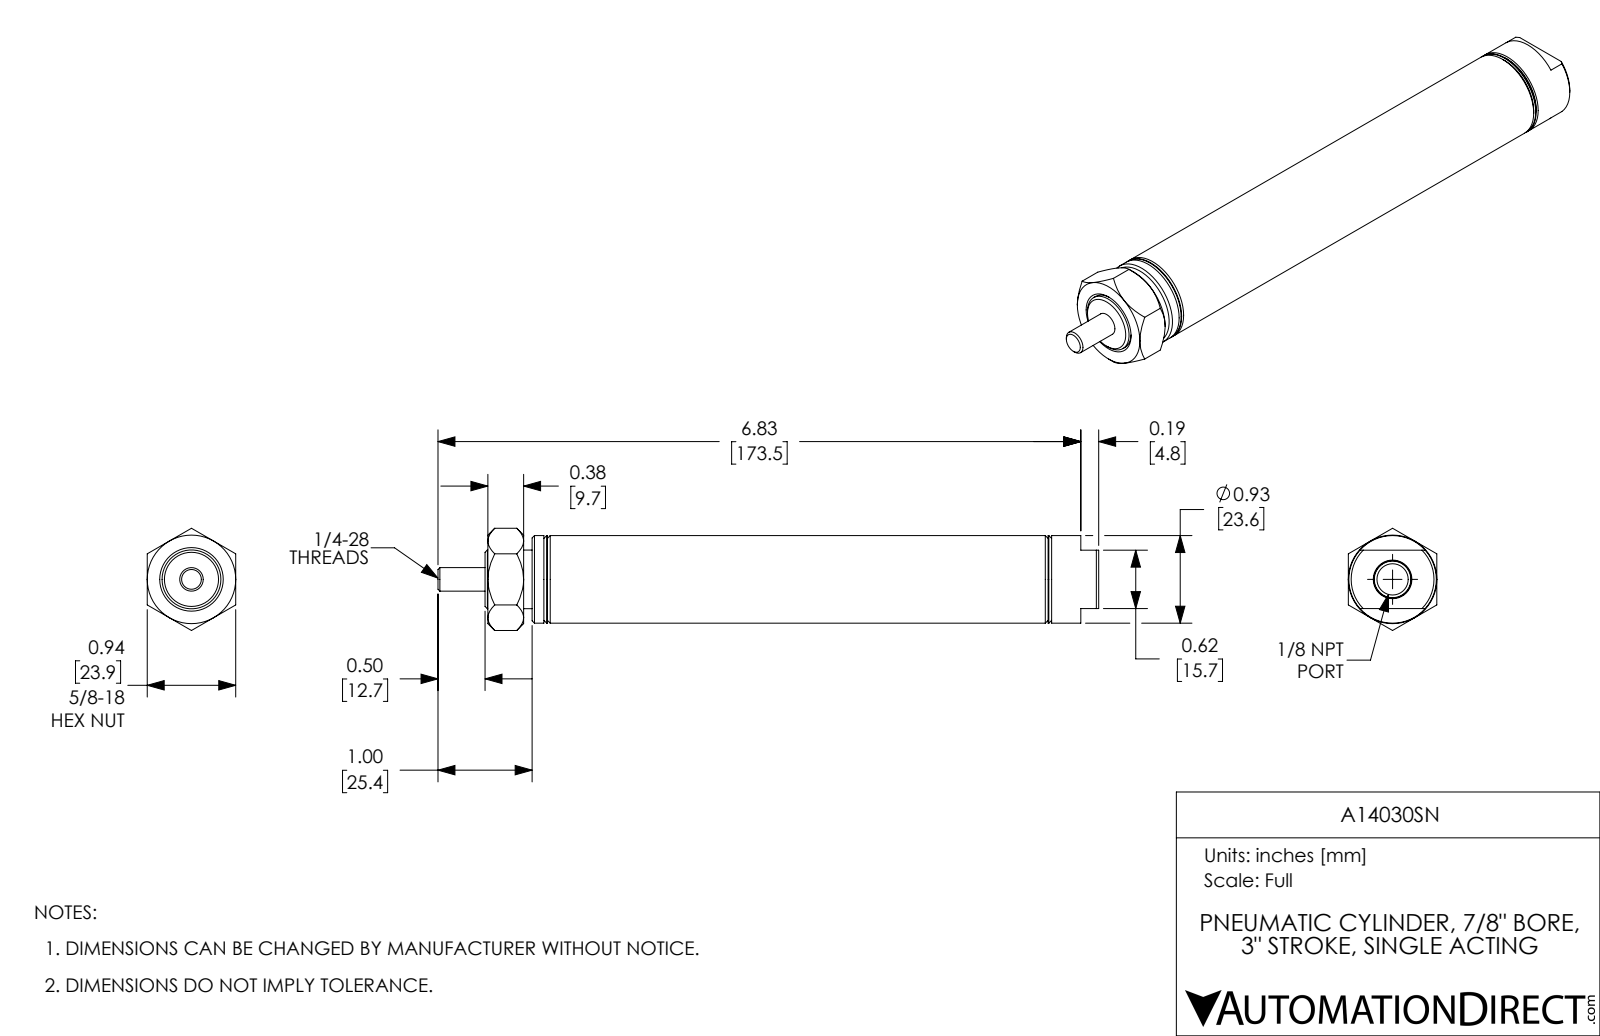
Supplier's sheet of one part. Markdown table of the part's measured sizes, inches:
| quantity | value |
| --- | --- |
| part name | A14030SN_Main Body; A14030SN; A14030SN_Mounting Nut_D-9; A14030SN_Rod |
| STEP written by | SolidWorks 2017 (AUTOMOTIVE_DESIGN) |
| units | inches |
| bodies | 3 solids, 94 faces (27 planar, 28 cylindrical, 39 other) |
| overall size | 7.02 × 1.085 × 0.94 |
| volume | 2.719 in³ |
| surface area | 41.83 in² |
| round holes (diameter × count) | 0.25 × 1, 0.332 × 1, 0.625 × 1, 0.875 × 1 |
| round bosses / shafts (diameter × count) | 0.93 × 1, 0.623 × 1, 0.562 × 1 |
| main face-to-face distances | 0.5, 3.5, 3, 0.94, 4.572, 1.448, 1.163, 4.663, 4.163, 6.02 |
